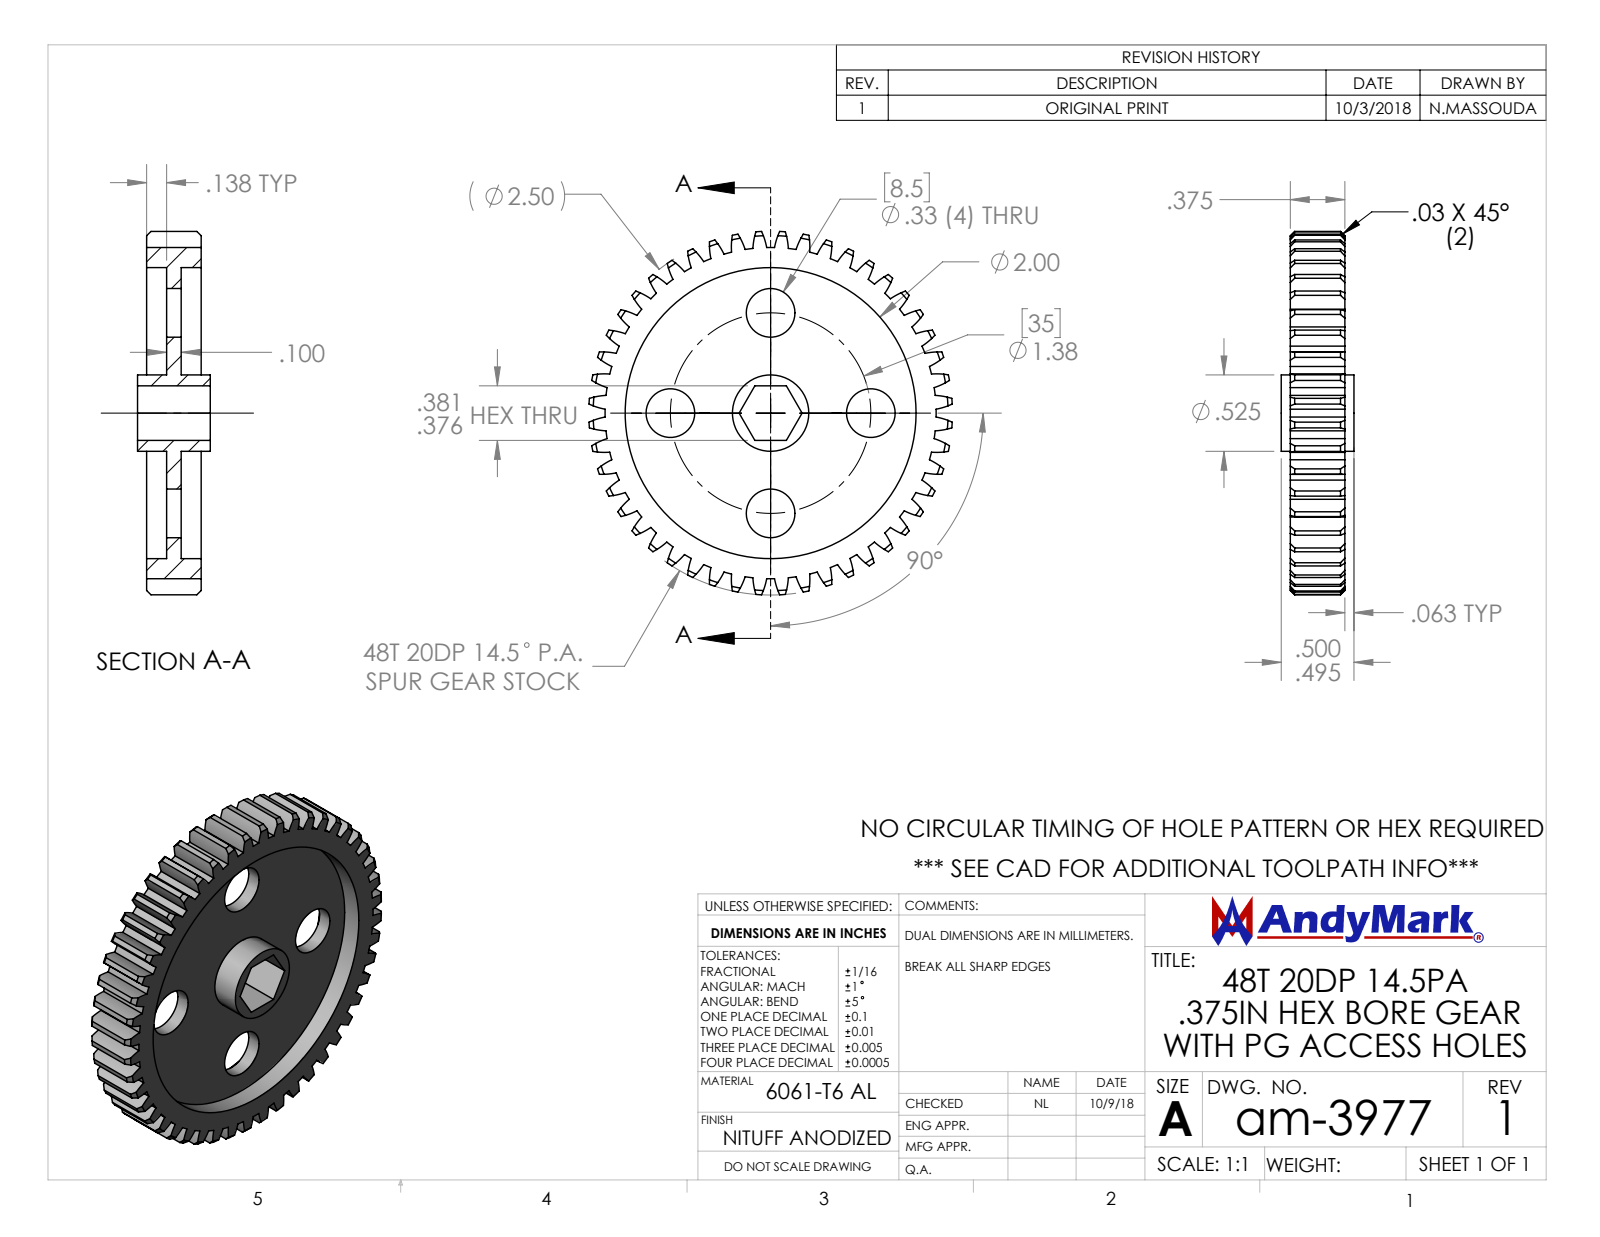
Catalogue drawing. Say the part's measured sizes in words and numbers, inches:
The part is named "am-3977 48T 20DP 375hex 375 FW With Holes". Its 3-D file was written by "SolidWorks 2018 (CONFIG_CONTROL_DESIGN)". It is 1 solid with 321 faces: 12 planar, 213 cylindrical and 96 other. Overall it measures 2.497 by 2.497 by 0.5 inches. Its volume is 0.796 cubic inches and its surface area 17.15 square inches. Round holes: 4 of diameter 0.335, 1 of diameter 2. Round bosses or shafts: 1 of diameter 0.525. Partial cylindrical surfaces (rounded edges, fillets, slot ends): 96 of radius 0.48, 1 of radius 1.138, 1 of radius 1.25. The main face-to-face distances are 0.1, 0.137, 0.237, 0.375, 0.238, 0.138, 0.375, 0.2, 0.3, 0.437. The hole center spacings are 0.689, 0.974, 1.378.
